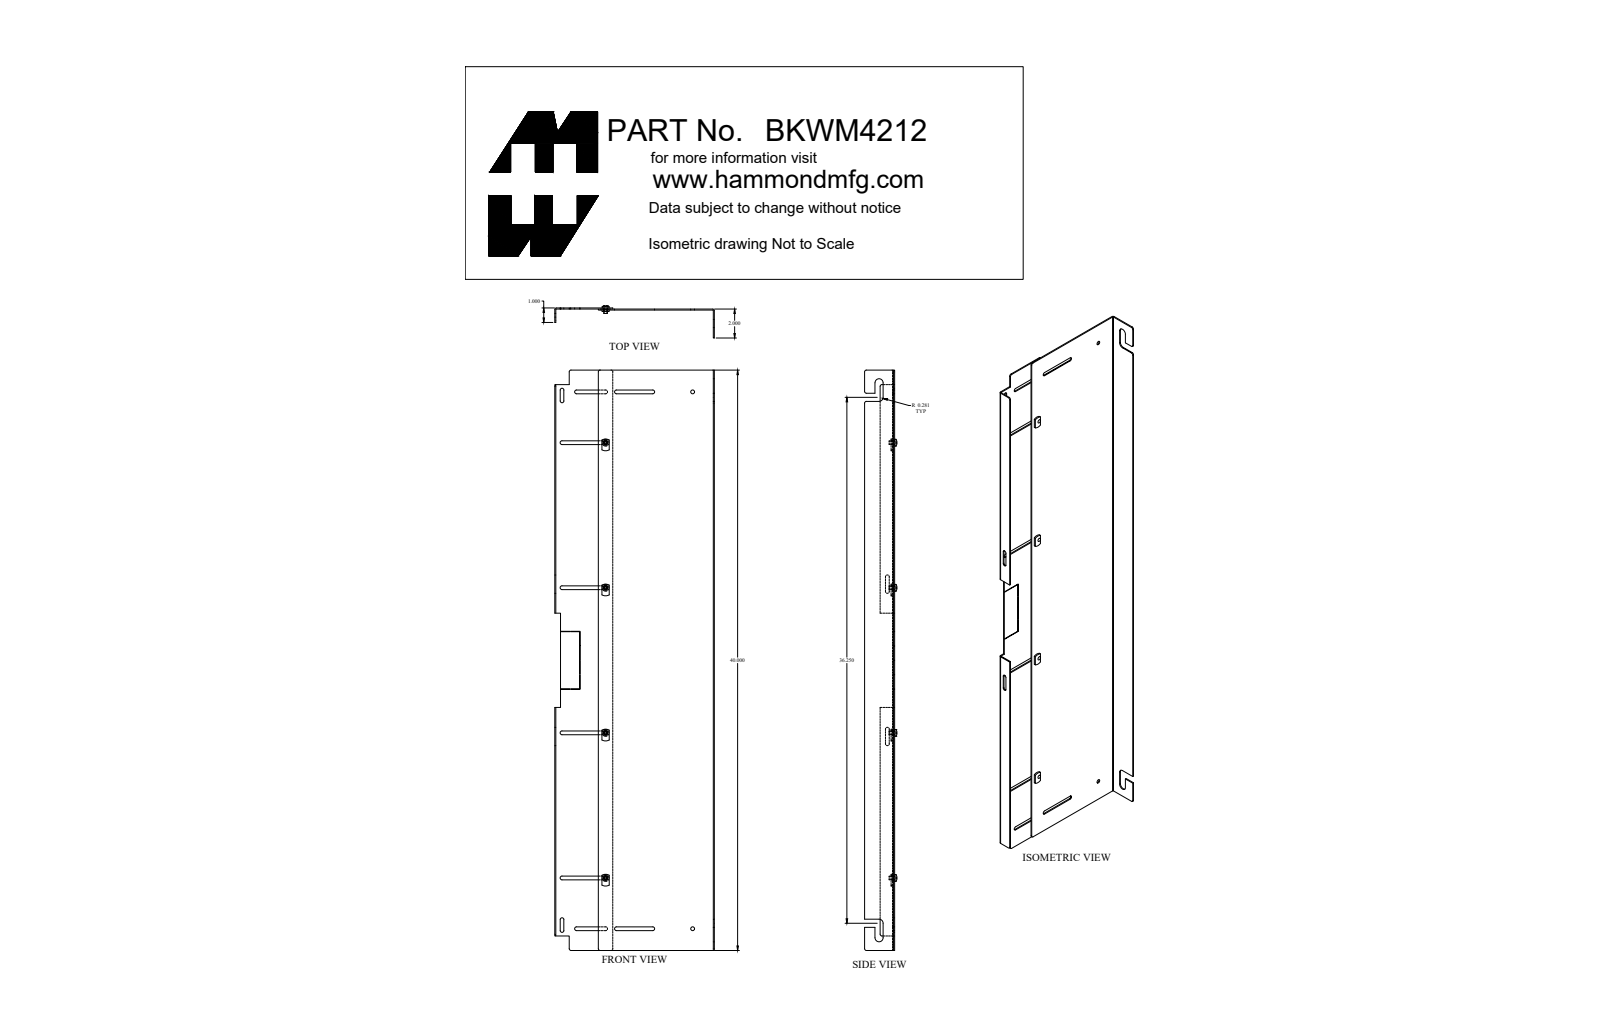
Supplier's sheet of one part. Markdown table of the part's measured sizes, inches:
| quantity | value |
| --- | --- |
| part name | BKWM4212_Default |
| STEP written by | SolidWorks 2019 (CONFIG_CONTROL_DESIGN) |
| units | inches |
| bodies | 10 solids, 313 faces (160 planar, 109 cylindrical, 44 other) |
| overall size | 40 × 11.005 × 2.237 |
| volume | 41.3 in³ |
| surface area | 1 167 in² |
| round holes (diameter × count) | 0.201 × 4, 0.313 × 4, 0.26 × 2 |
| round bosses / shafts (diameter × count) | 0.468 × 4, 0.293 × 4, 0.25 × 4 |
| partial cylindrical surfaces (radius × count) | 0.13 × 20, 0.125 × 16, 0.5 × 8, 0.281 × 4, 0.036 × 2, 0.108 × 2 |
| main face-to-face distances | 0.072, 0.144, 10.933, 11.005, 10.861, 4, 3.928, 6.933, 7.005, 3.005 |
| hole center spacings | 10, 6.946, 14.773, 20, 24.254, 34.033, 30, 37 |
